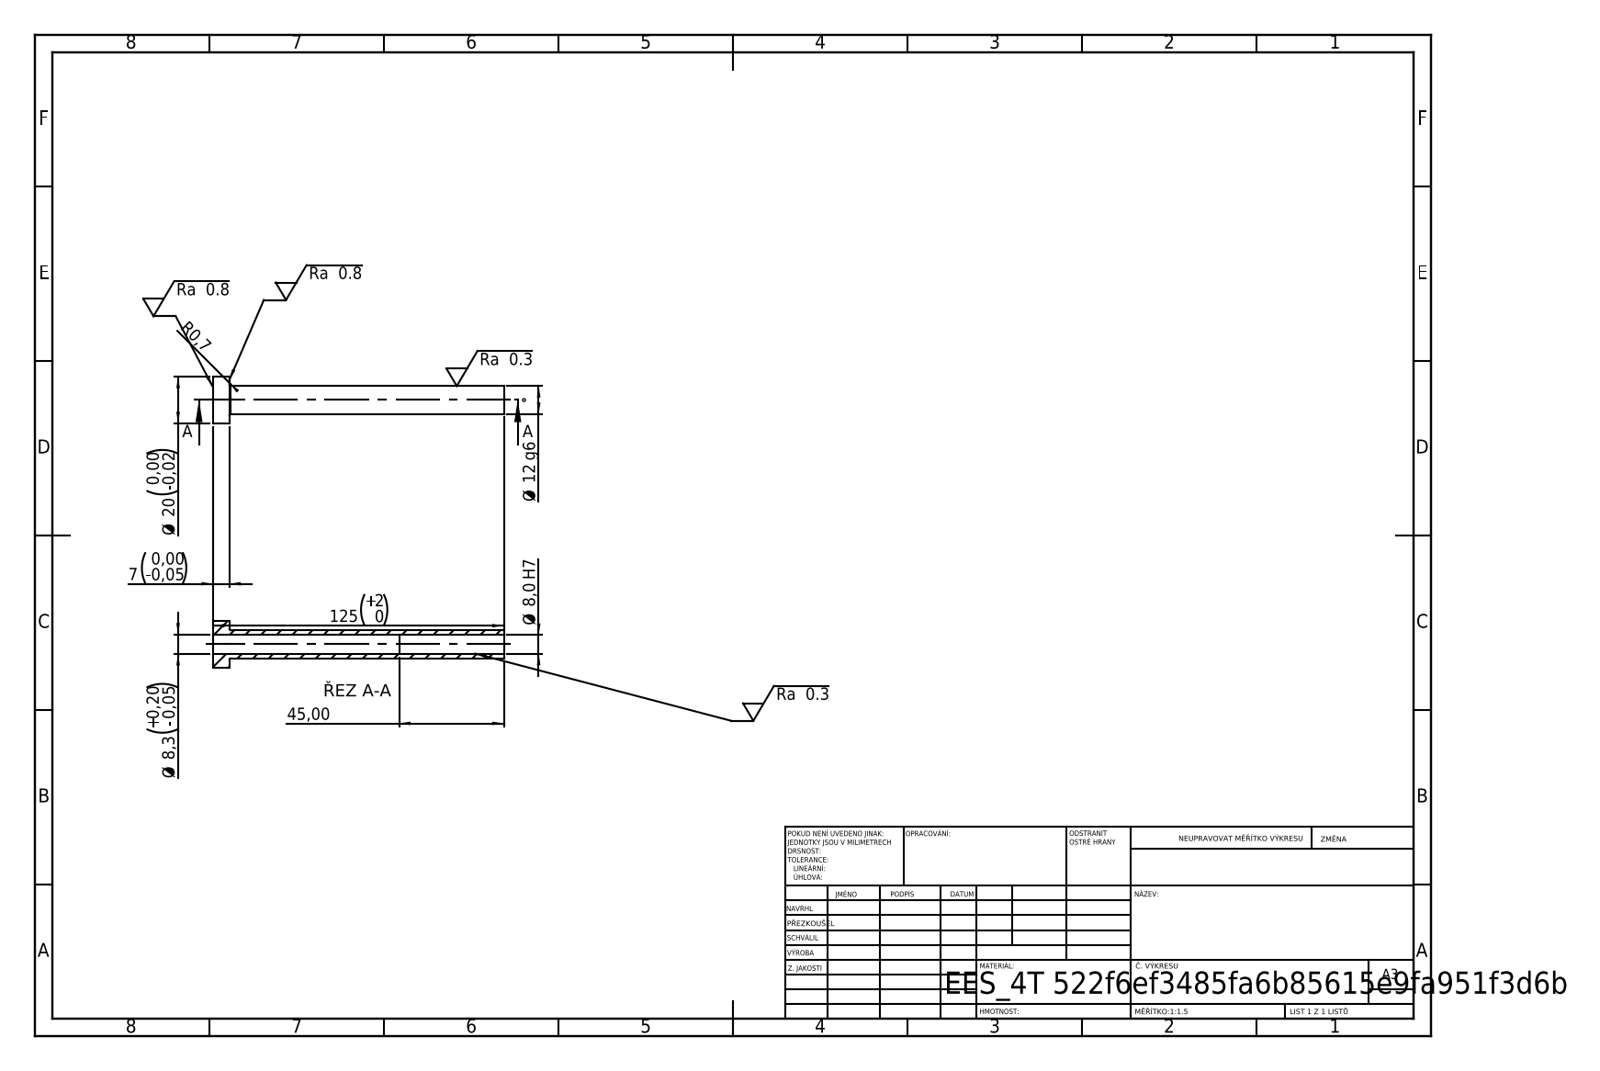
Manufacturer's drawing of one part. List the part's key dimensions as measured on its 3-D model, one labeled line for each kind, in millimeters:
STEP written by: SolidWorks 2019 (CONFIG_CONTROL_DESIGN)
Units: millimetres
Bodies: 1 solid, 14 faces (4 planar, 8 cylindrical, 2 other)
Overall size (bounding box): 125 × 20 × 20
Volume: 8 958 mm³ · Surface area: 8 622 mm²
Round holes (diameter × count): ⌀8 ×1, ⌀8.3 ×1
Round bosses / shafts (diameter × count): ⌀20 ×1, ⌀12 ×1
Main face-to-face distances: 7, 125, 118, 80, 73, 45
